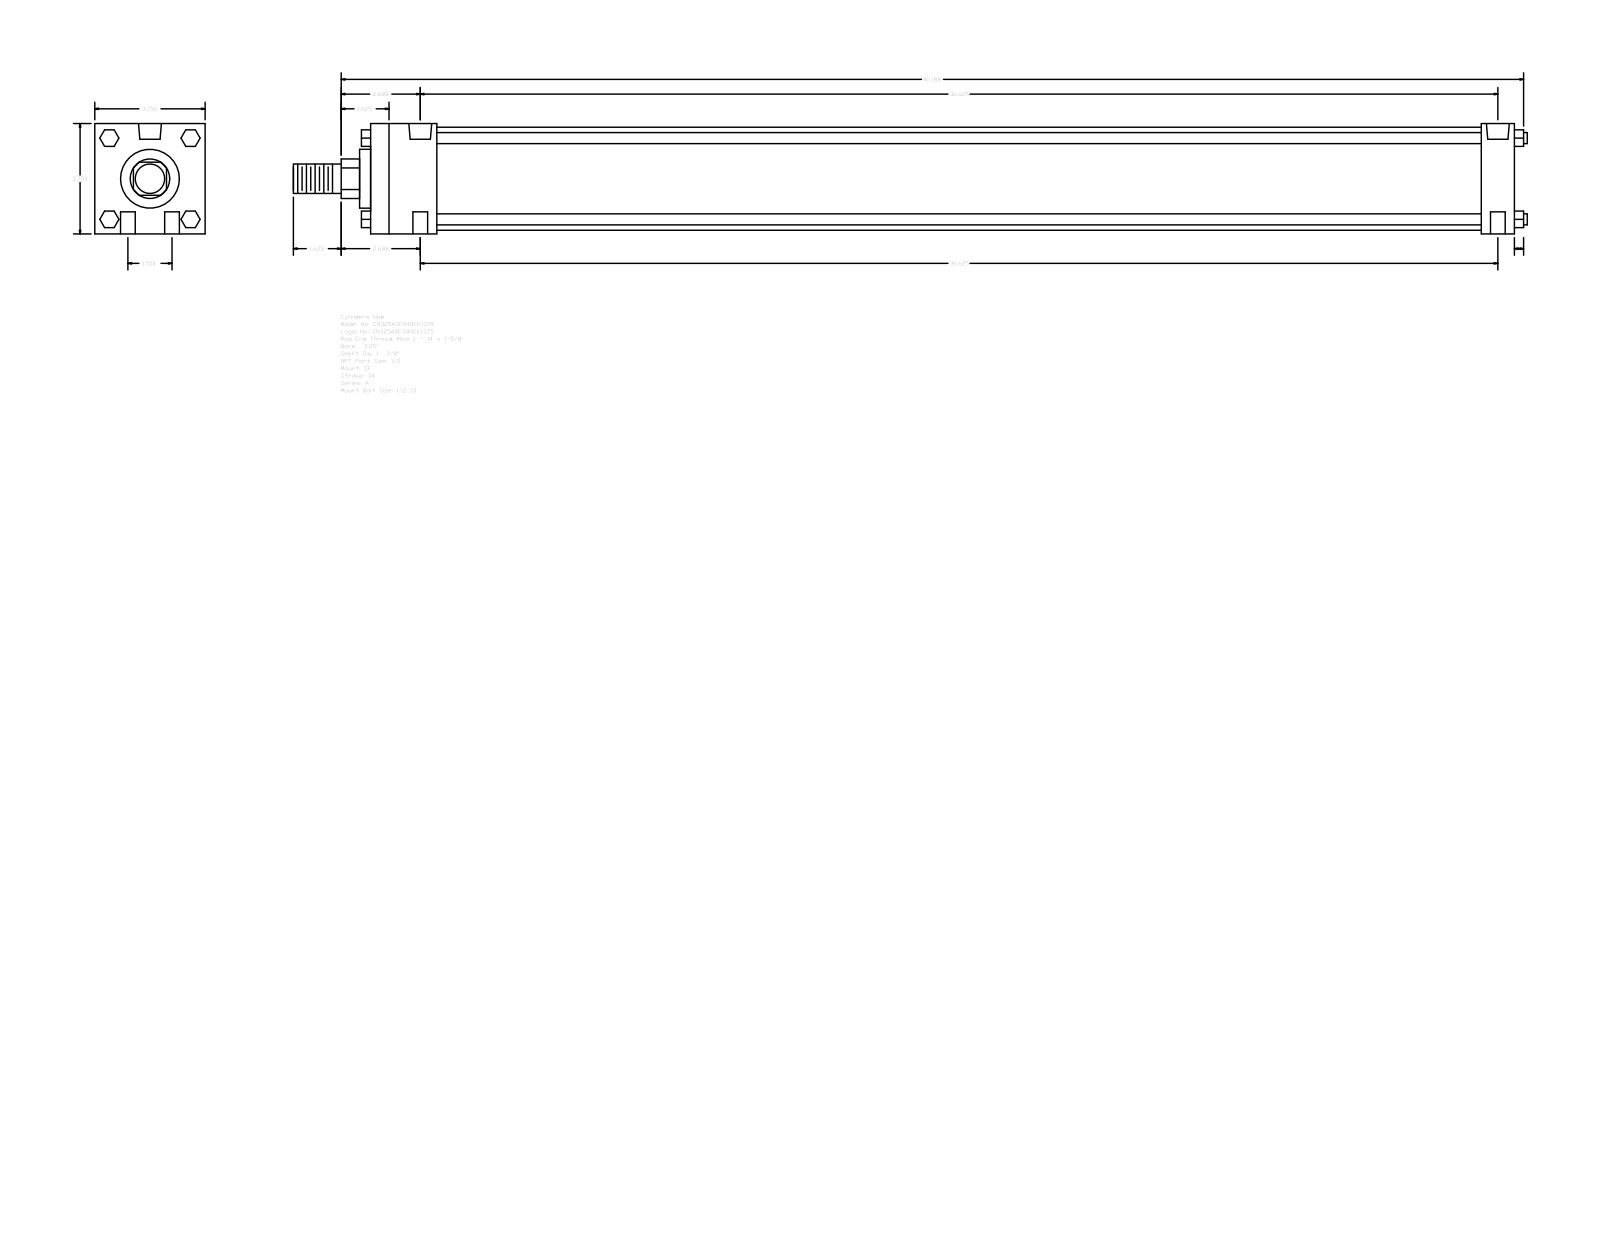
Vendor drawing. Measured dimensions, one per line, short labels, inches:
name: A_SF__0325_1.375
written by: GSSL Pune (CONFIG_CONTROL_DESIGN)
unit: in
bodies: 0 solids, 124 faces (94 planar, 30 cylindrical, 0 other)
size: 41.937 × 3.75 × 3.75
holes: 4× ⌀0.5, 2× ⌀0.344, 2× ⌀0.778
bosses: 4× ⌀0.375, 1× ⌀3.5, 1× ⌀2, 1× ⌀1.375, 1× ⌀1
rounds: 1× R0.672
face distances: 3.75, 38.875, 2.25, 1.125, 37.75, 35.5, 36.625, 2.625, 0.375, 38.125
hole spacings: 0.75, 36.633, 36.625, 1.5, 36.656, 36.375
